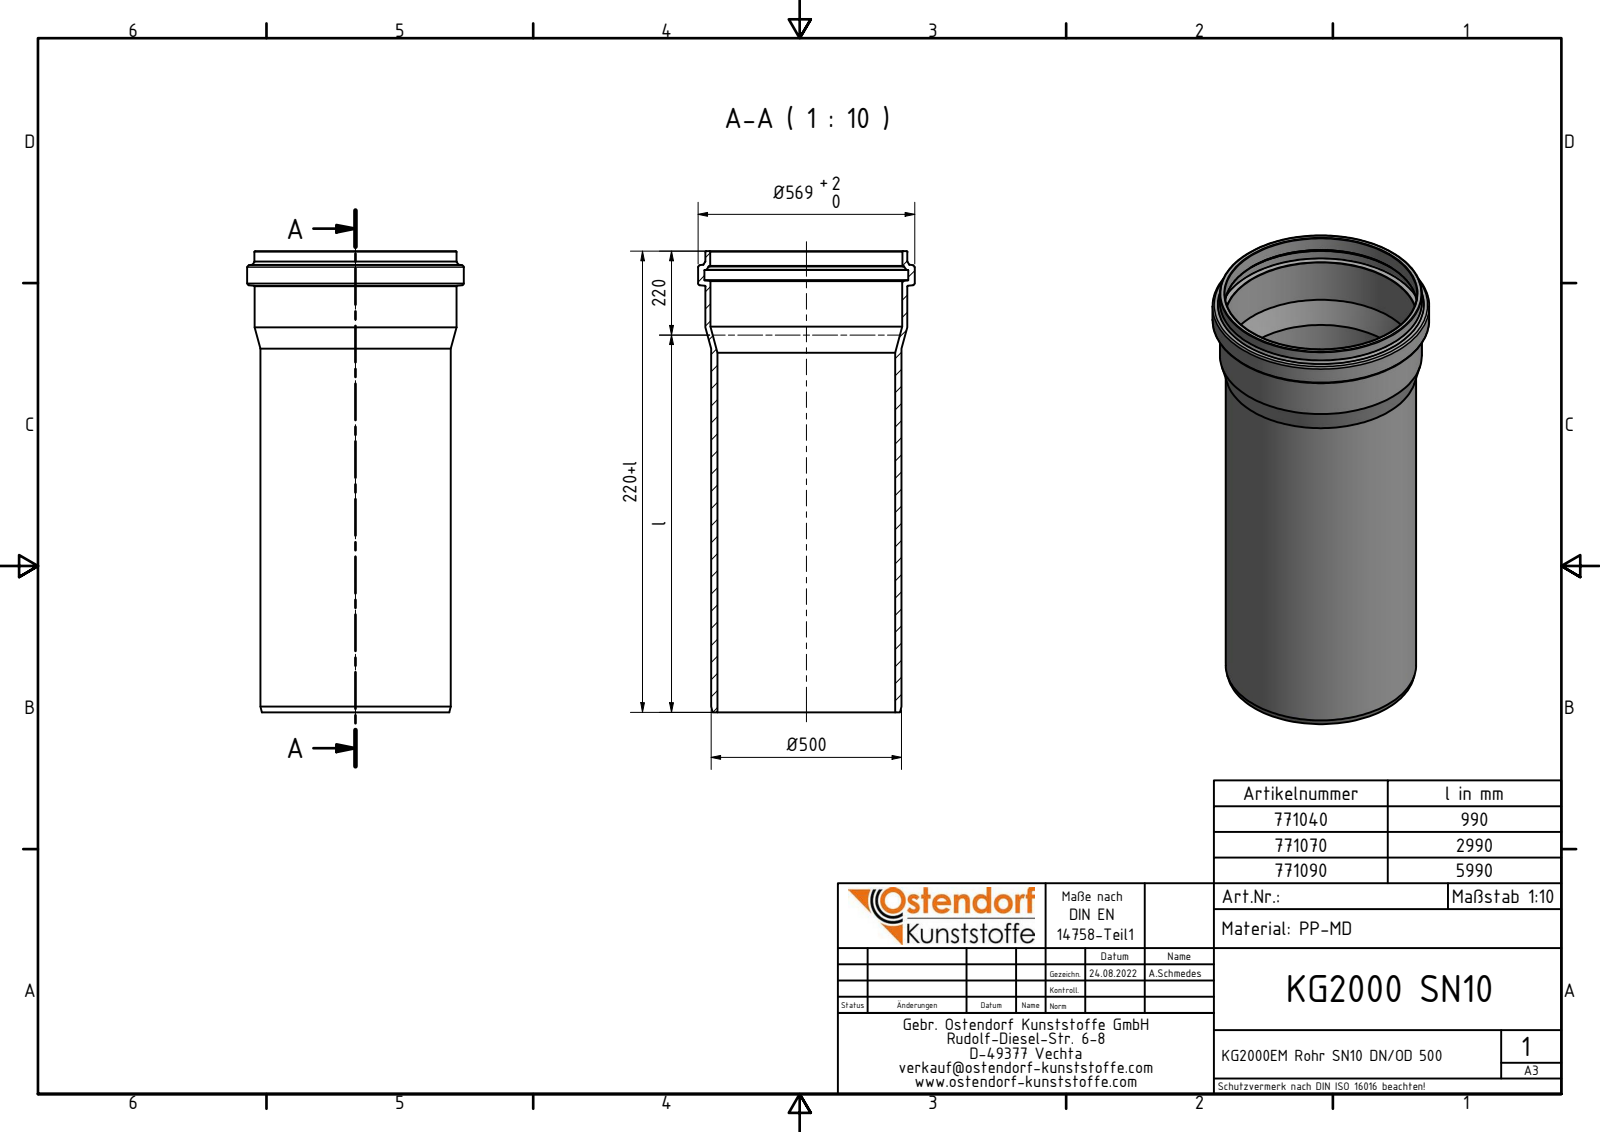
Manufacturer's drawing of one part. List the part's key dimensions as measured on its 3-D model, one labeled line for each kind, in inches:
Part name (STEP PRODUCT): 771070 KG2000EM Rohr SN10 DN-OD 500x3000
STEP written by: Autodesk Inventor 2020 (AUTOMOTIVE_DESIGN)
Units: inches
Bodies: 1 solid, 33 faces (2 planar, 8 cylindrical, 23 other)
Overall size (bounding box): 126.378 × 22.402 × 22.402
Volume: 4 909 in³ · Surface area: 15 410 in²
Round holes (diameter × count): ⌀18.386 ×1, ⌀19.823 ×1, ⌀19.862 ×1, ⌀21.063 ×1
Round bosses / shafts (diameter × count): ⌀22.402 ×1, ⌀20.886 ×1, ⌀20.866 ×1, ⌀19.685 ×1
Main face-to-face distances: 126.378
